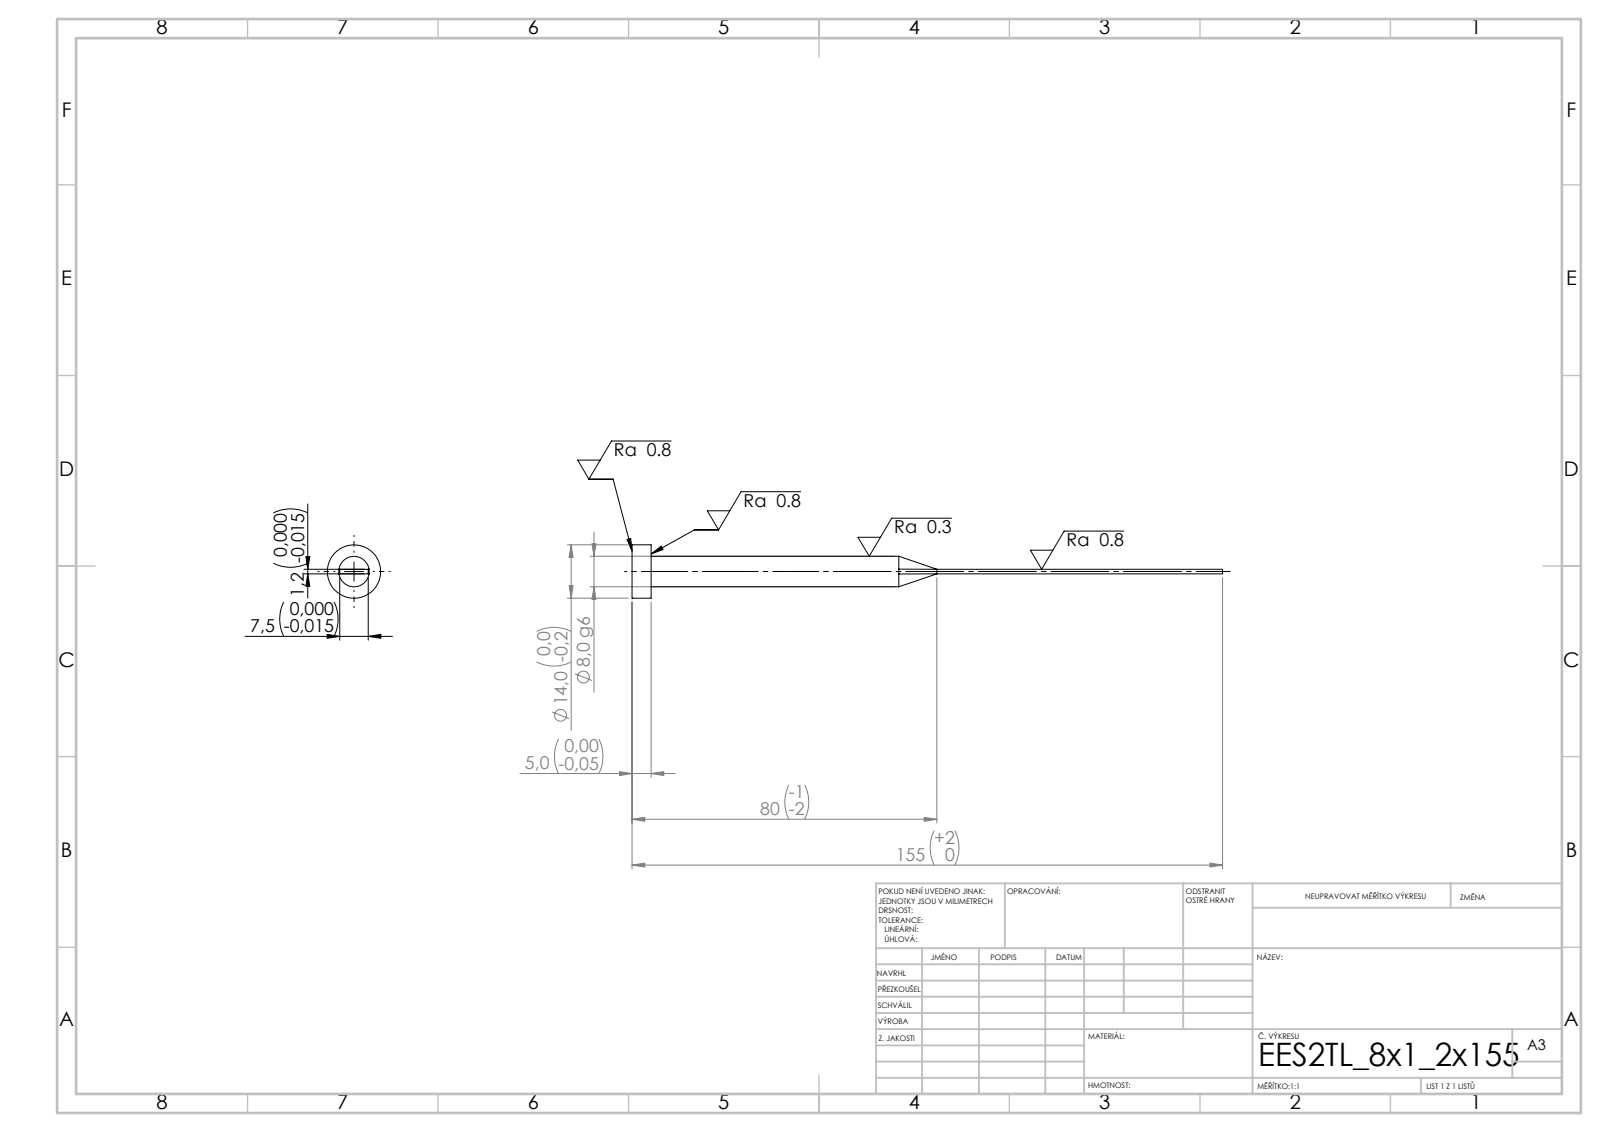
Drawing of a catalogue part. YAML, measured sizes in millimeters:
step_written_by: "SolidWorks 2019 (CONFIG_CONTROL_DESIGN)"
units: millimeters
bodies: {solids: 1, faces: 15, planar: 7, cylindrical: 4, other: 4}
overall_size: [155, 14, 14]
volume: 4991
surface_area: 3633
round_bosses_or_shafts:
  - {diameter: 14, count: 1}
  - {diameter: 8, count: 1}
face_to_face_distances: [1.2, 5, 7.5, 155, 150]
